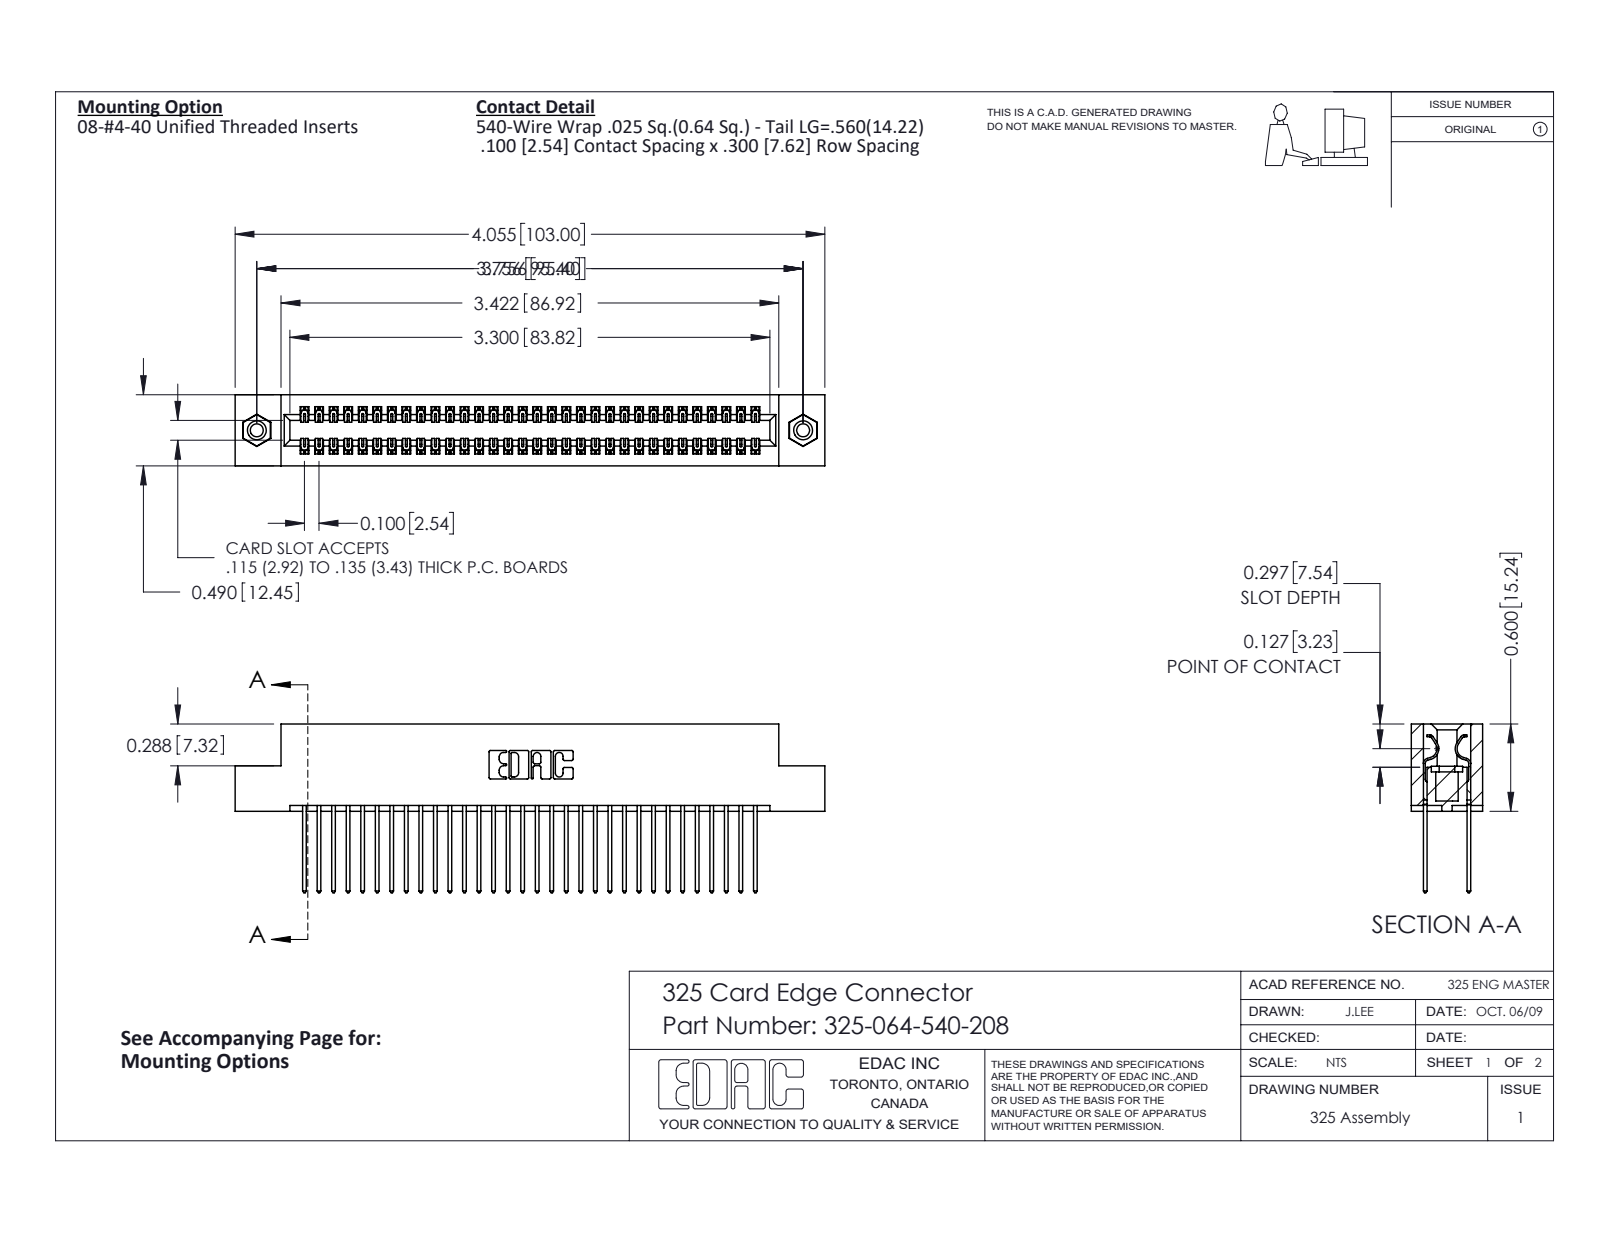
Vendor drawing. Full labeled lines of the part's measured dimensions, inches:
Part name (STEP PRODUCT): 325-064-540-208; 345-250-001_345-250-003-102; 325-292-001_325-293-140; 325 Part_TI
STEP written by: SolidWorks 2016 (CONFIG_CONTROL_DESIGN)
Units: inches
Bodies: 67 solids, 3502 faces (2406 planar, 1080 cylindrical, 16 other)
Overall size (bounding box): 4.055 × 1.16 × 0.49
Volume: 0.82 in³ · Surface area: 26.66 in²
Round holes (diameter × count): ⌀0.089 ×2, ⌀0.125 ×2, ⌀0.16 ×2
Round bosses / shafts (diameter × count): ⌀0.155 ×2
Partial cylindrical surfaces — rounded edges, fillets, slot ends (radius × count): R0.006 ×96, R0.01 ×64, R0.01 ×22, R0.007 ×6, R0.031 ×6, R0.026 ×3, R0.014 ×2, R0.022 ×2
Main face-to-face distances: 0.083, 0.407, 0.3, 0.107, 0.383, 0.025, 0.49, 0.325, 0.275, 0.04
Hole centre spacings: 3.756
